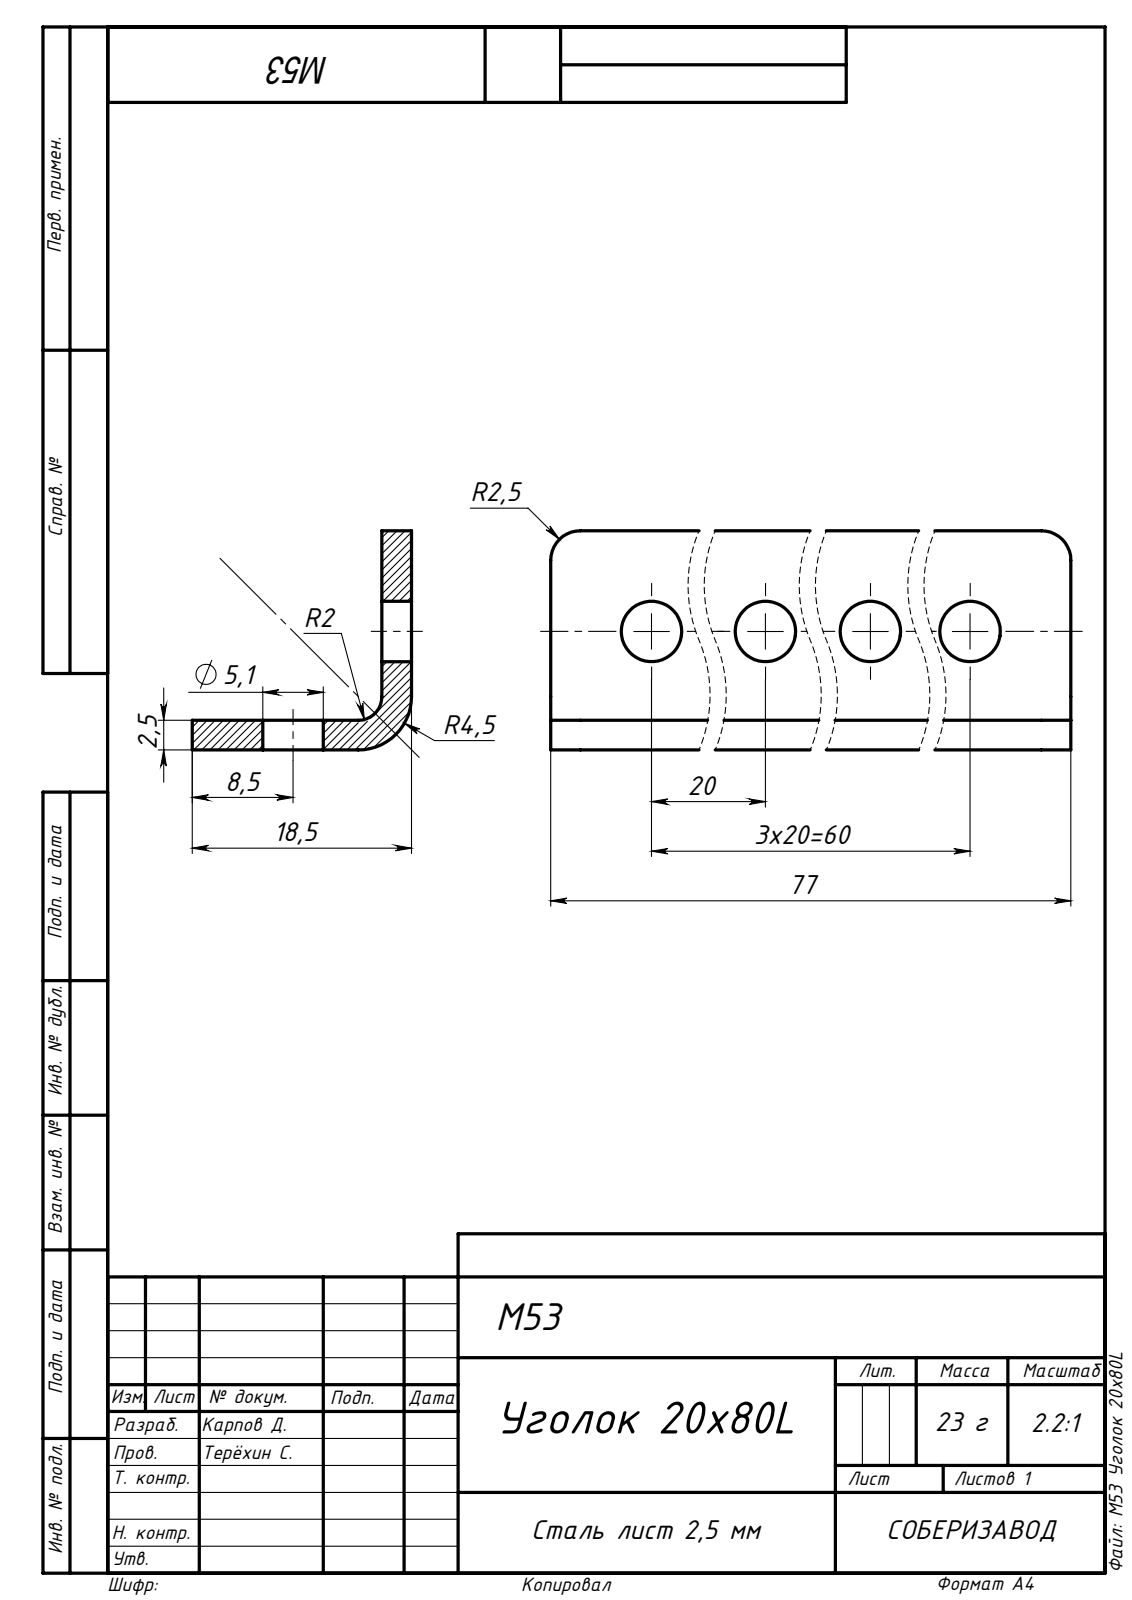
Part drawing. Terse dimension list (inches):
written by: SolidWorks 2021 (AUTOMOTIVE_DESIGN)
unit: in
bodies: 1 solid, 34 faces (12 planar, 22 cylindrical, 0 other)
size: 3.031 × 0.728 × 0.728
volume: 0.363 in³; area: 8.713 in²
holes: 8× ⌀0.201
rounds: 4× R0.098, 1× R0.079, 1× R0.177
face distances: 0.098, 0.728, 0.63, 3.031
hole spacings: 0.787, 1.575, 2.362
